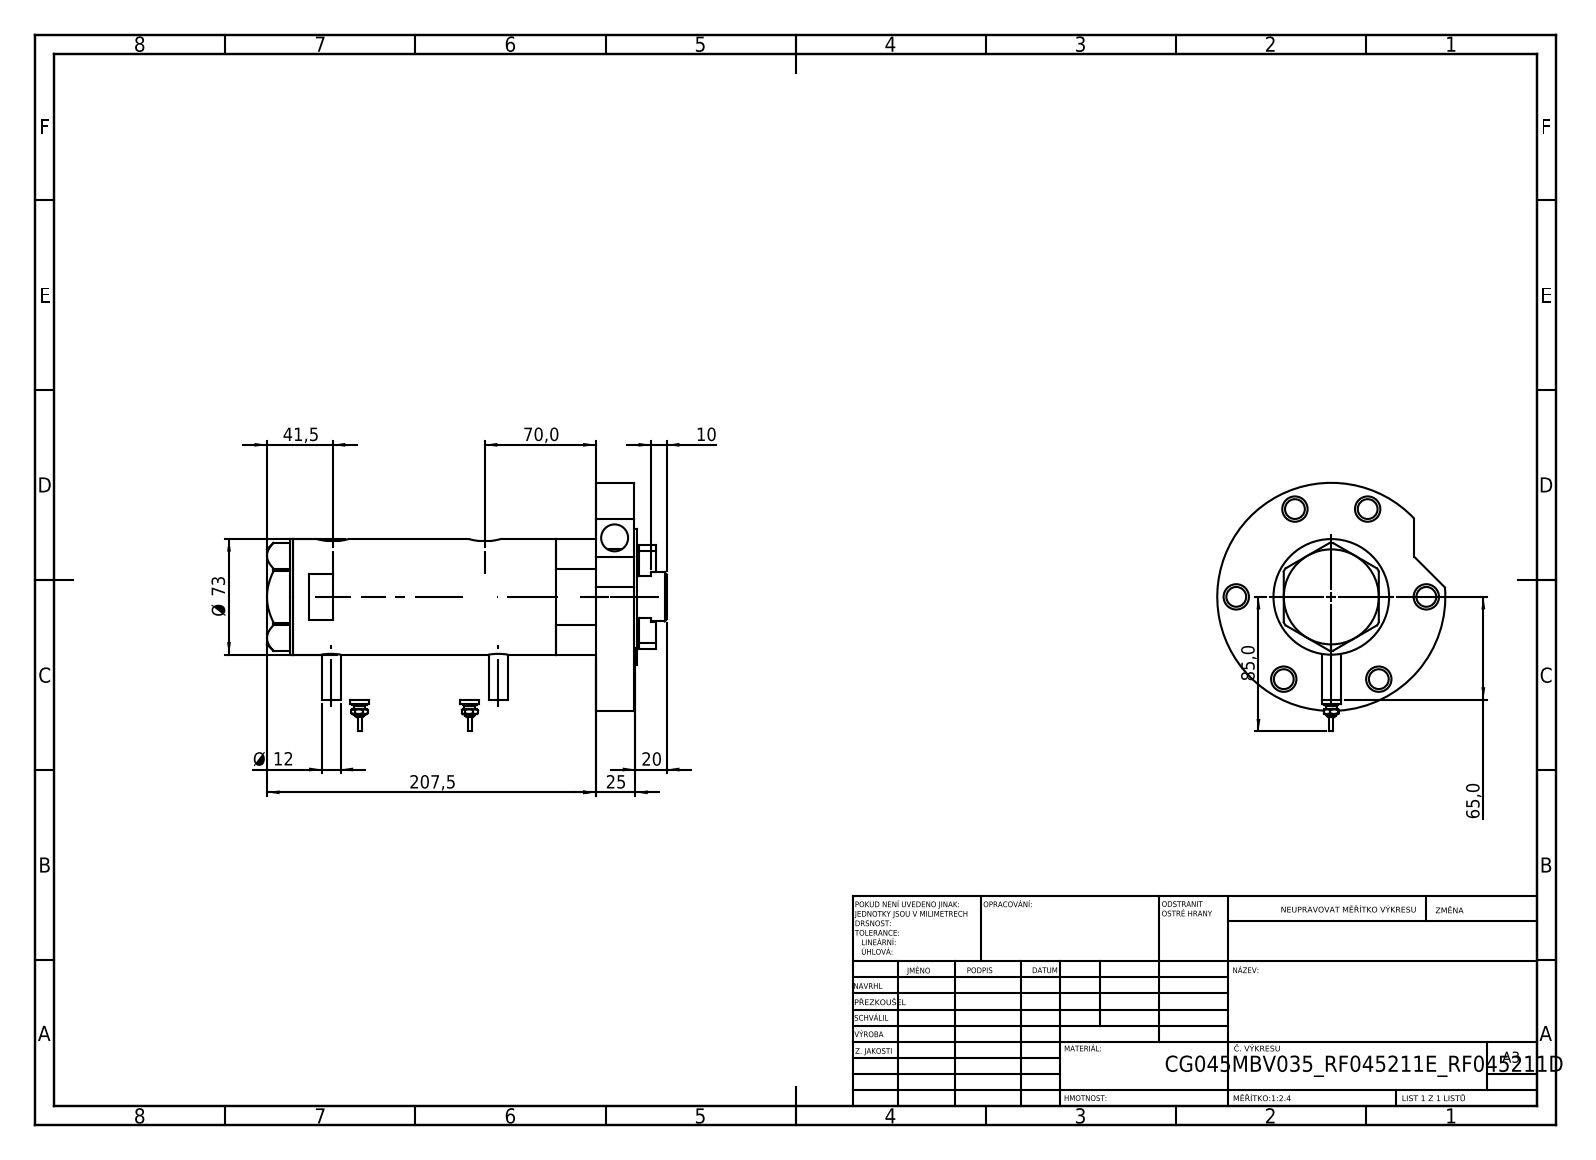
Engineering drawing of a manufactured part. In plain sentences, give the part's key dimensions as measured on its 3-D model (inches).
The part is named "V270CG_RF211D; V270CG_RF211E; V270CG_VC; V270CG_BACK (+3 more)". Its 3-D file was written by "SolidWorks 2019 (CONFIG_CONTROL_DESIGN)". It is 9 solids with 296 faces: 112 planar, 120 cylindrical and 64 other. Overall it measures 9.941 by 6.181 by 5.669 inches. Its volume is 72.31 cubic inches and its surface area 326.6 square inches. Round holes: 8 of diameter 0.492, 6 of diameter 0.63, 4 of diameter 0.319, 4 of diameter 0.531, 2 of diameter 0.518, 1 of diameter 0.413, 1 of diameter 0.669, 1 of diameter 1.26, 1 of diameter 1.319, 1 of diameter 1.772, 1 of diameter 1.89, 1 of diameter 2.362. Round bosses or shafts: 4 of diameter 0.472, 2 of diameter 0.354, 2 of diameter 0.276, 2 of diameter 0.177, 2 of diameter 0.098, 1 of diameter 5.669, 1 of diameter 3.386, 1 of diameter 2.874. Partial cylindrical surfaces (rounded edges, fillets, slot ends): 2 of radius 0.394. The main face-to-face distances are 0.945, 7.52, 1.024, 3.74, 0.079, 8.465, 8.543, 0.039, 4.764, 2.756. The hole center spacings are 2.362, 0.99, 2.272, 2.82, 0.591, 1.38, 1.413, 1.724.
